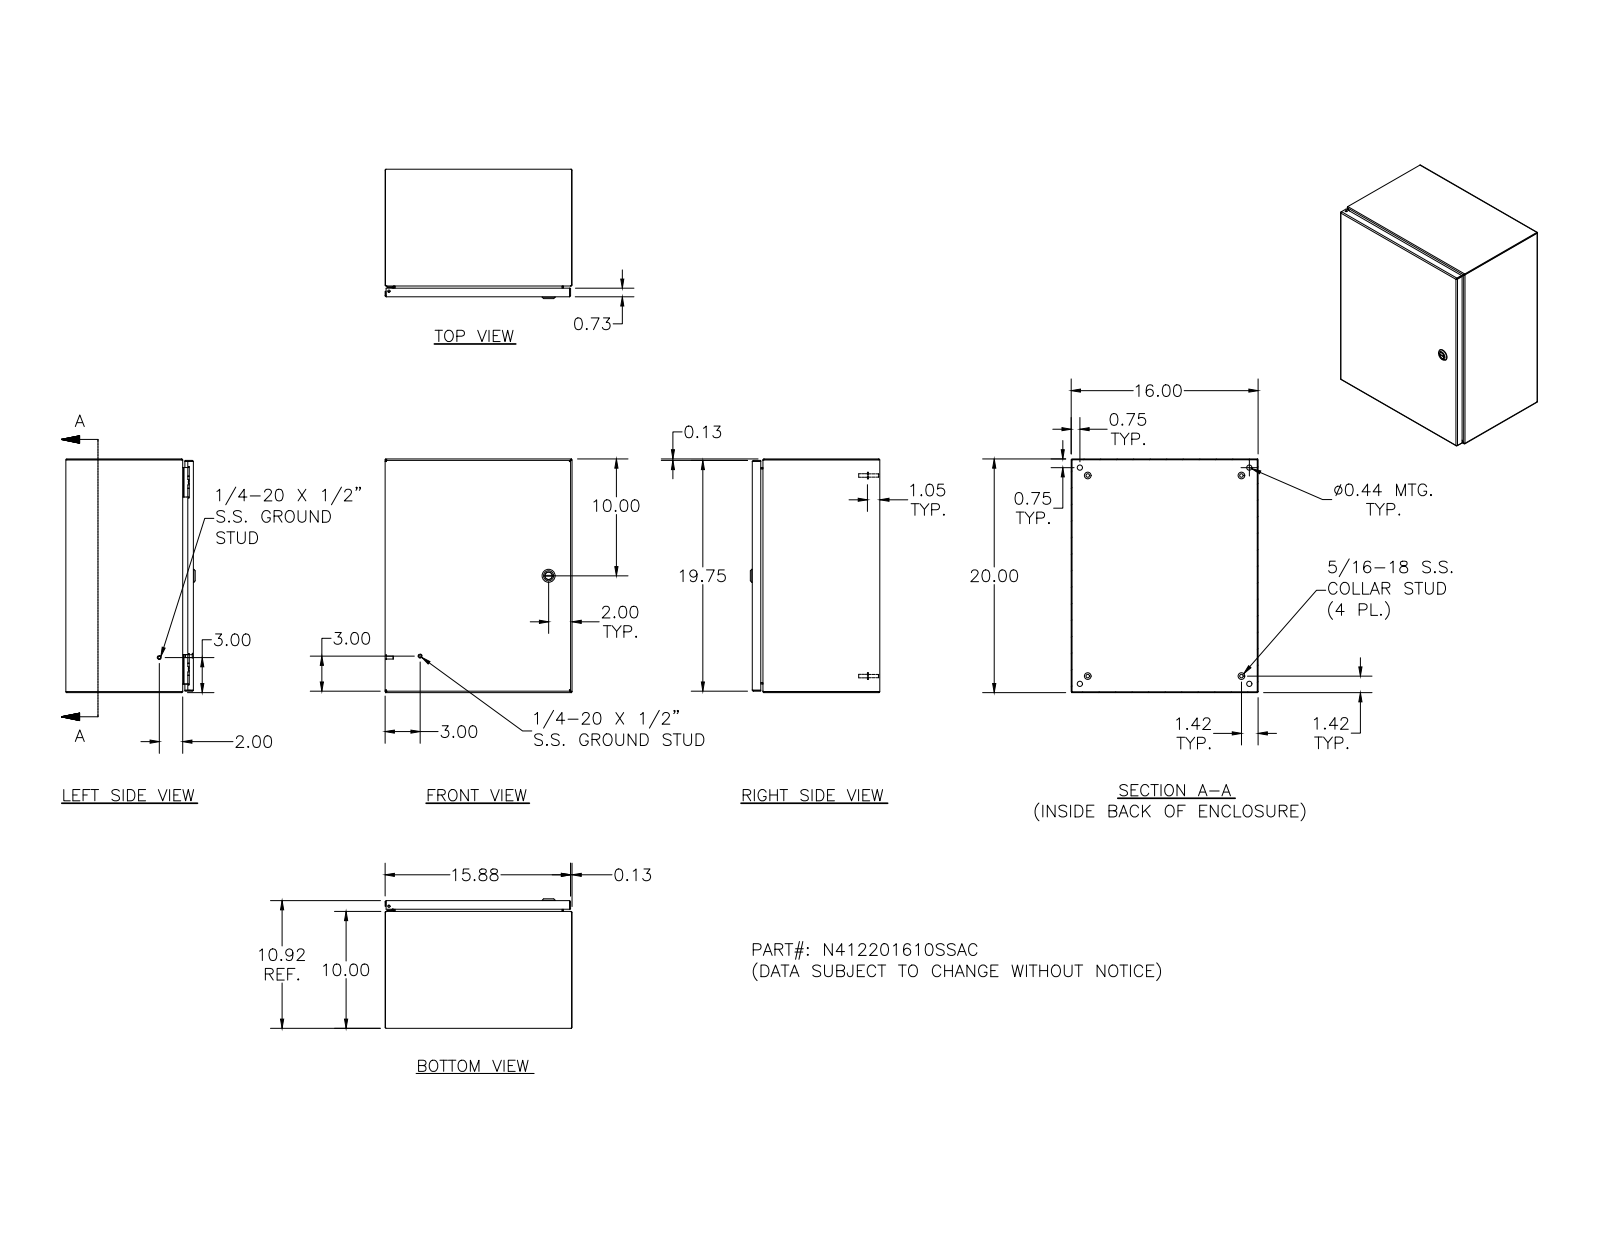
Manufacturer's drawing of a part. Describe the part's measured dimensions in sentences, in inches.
The part is named "N412201610SSAC; N412201610SSACBKP; 388151; N4122016SSACLID (+8 more)". Its 3-D file was written by "Autodesk Inventor 2011 (AUTOMOTIVE_DESIGN)". It is 34 solids with 1364 faces: 523 planar, 497 cylindrical and 344 other. Overall it measures 20 by 16 by 11.075 inches. Its volume is 111.7 cubic inches and its surface area 3 037 square inches. Round holes: 5 of diameter 0.188, 4 of diameter 0.093, 4 of diameter 0.152, 4 of diameter 0.167, 4 of diameter 0.172, 4 of diameter 0.437, 2 of diameter 0.156, 1 of diameter 0.187, 1 of diameter 0.197, 1 of diameter 0.315, 1 of diameter 0.394, 1 of diameter 0.402. Round bosses or shafts: 10 of diameter 0.25, 4 of diameter 0.563, 4 of diameter 0.36, 4 of diameter 0.32, 4 of diameter 0.3, 4 of diameter 0.275, 4 of diameter 0.256, 4 of diameter 0.164. Partial cylindrical surfaces (rounded edges, fillets, slot ends): 26 of radius 0.05, 18 of radius 0.016, 16 of radius 0.016, 16 of radius 0.09, 14 of radius 0.031, 14 of radius 0.125, 9 of radius 0.02, 8 of radius 0.032. The main face-to-face distances are 0.074, 10.843, 15.926, 19.926, 10.769, 10.917, 16, 15.852, 20, 19.852. The hole center spacings are 16, 0.017, 0.66, 16.008, 0.019, 0.5, 0.648, 0.652.
